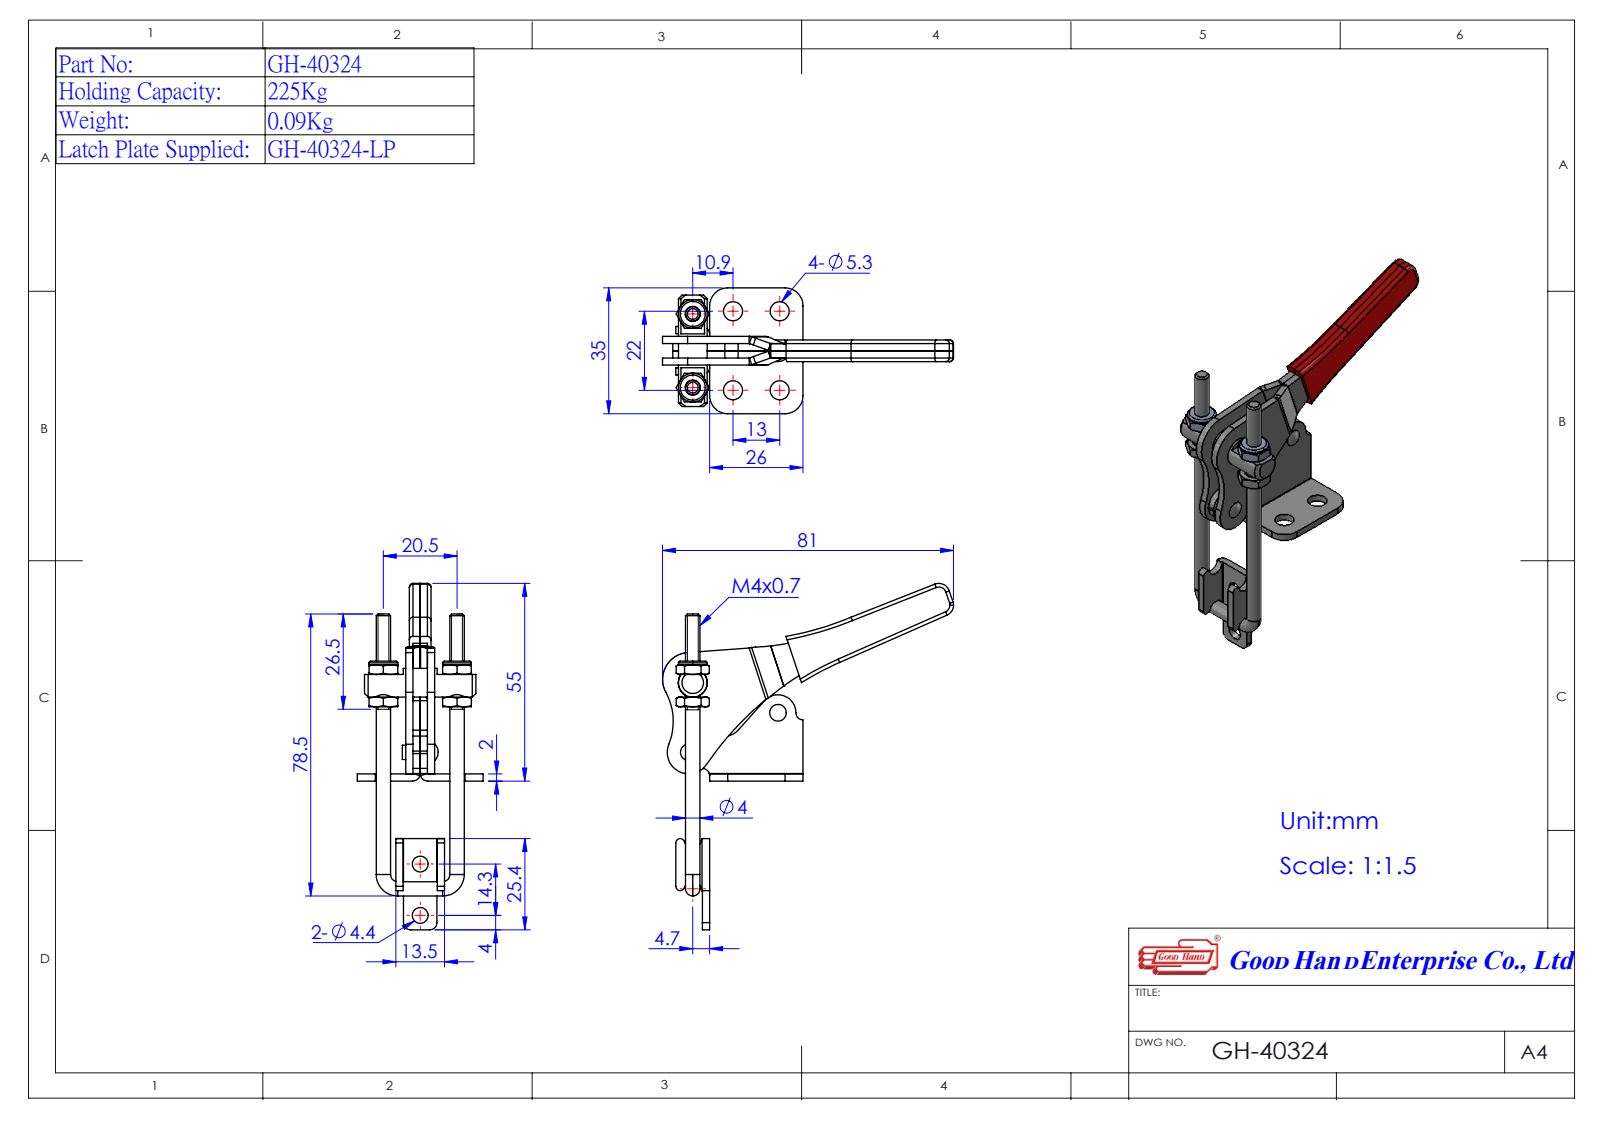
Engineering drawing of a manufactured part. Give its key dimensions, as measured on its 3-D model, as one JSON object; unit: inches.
{"part_name": "GH-40324(簡化); 44032444-1^GH-40324(簡化); 14032414-1^GH-40324(簡化); Group2^GH-40324(簡化) (+2 more)", "step_written_by": "SolidWorks 2016 (AUTOMOTIVE_DESIGN)", "units": "inches", "bodies": {"solids": 7, "faces": 345, "planar": 126, "cylindrical": 133, "other": 86}, "overall_size": [3.795, 3.189, 1.378], "volume_in3": 0.869, "surface_area_in2": 20.78, "round_holes": [[0.209, 4], [0.12, 2], [0.165, 2], [0.173, 2], [0.177, 2], [0.197, 2], [0.315, 1]], "round_bosses_or_shafts": [[0.157, 5], [0.315, 2]], "partial_cylinders_radius": [[0.004, 8], [0.083, 8], [0.197, 6], [3.359, 3], [3.524, 3], [0.047, 2], [0.098, 2], [0.118, 2]], "face_to_face_distances": [0.079, 0.039, 0.236, 0.157, 0.276, 0.197, 0.315, 0.344, 0.108, 0.423], "hole_center_spacings": [0.442, 0.512, 0.866, 0.946, 0.953, 1.006, 1.268, 0.563]}
